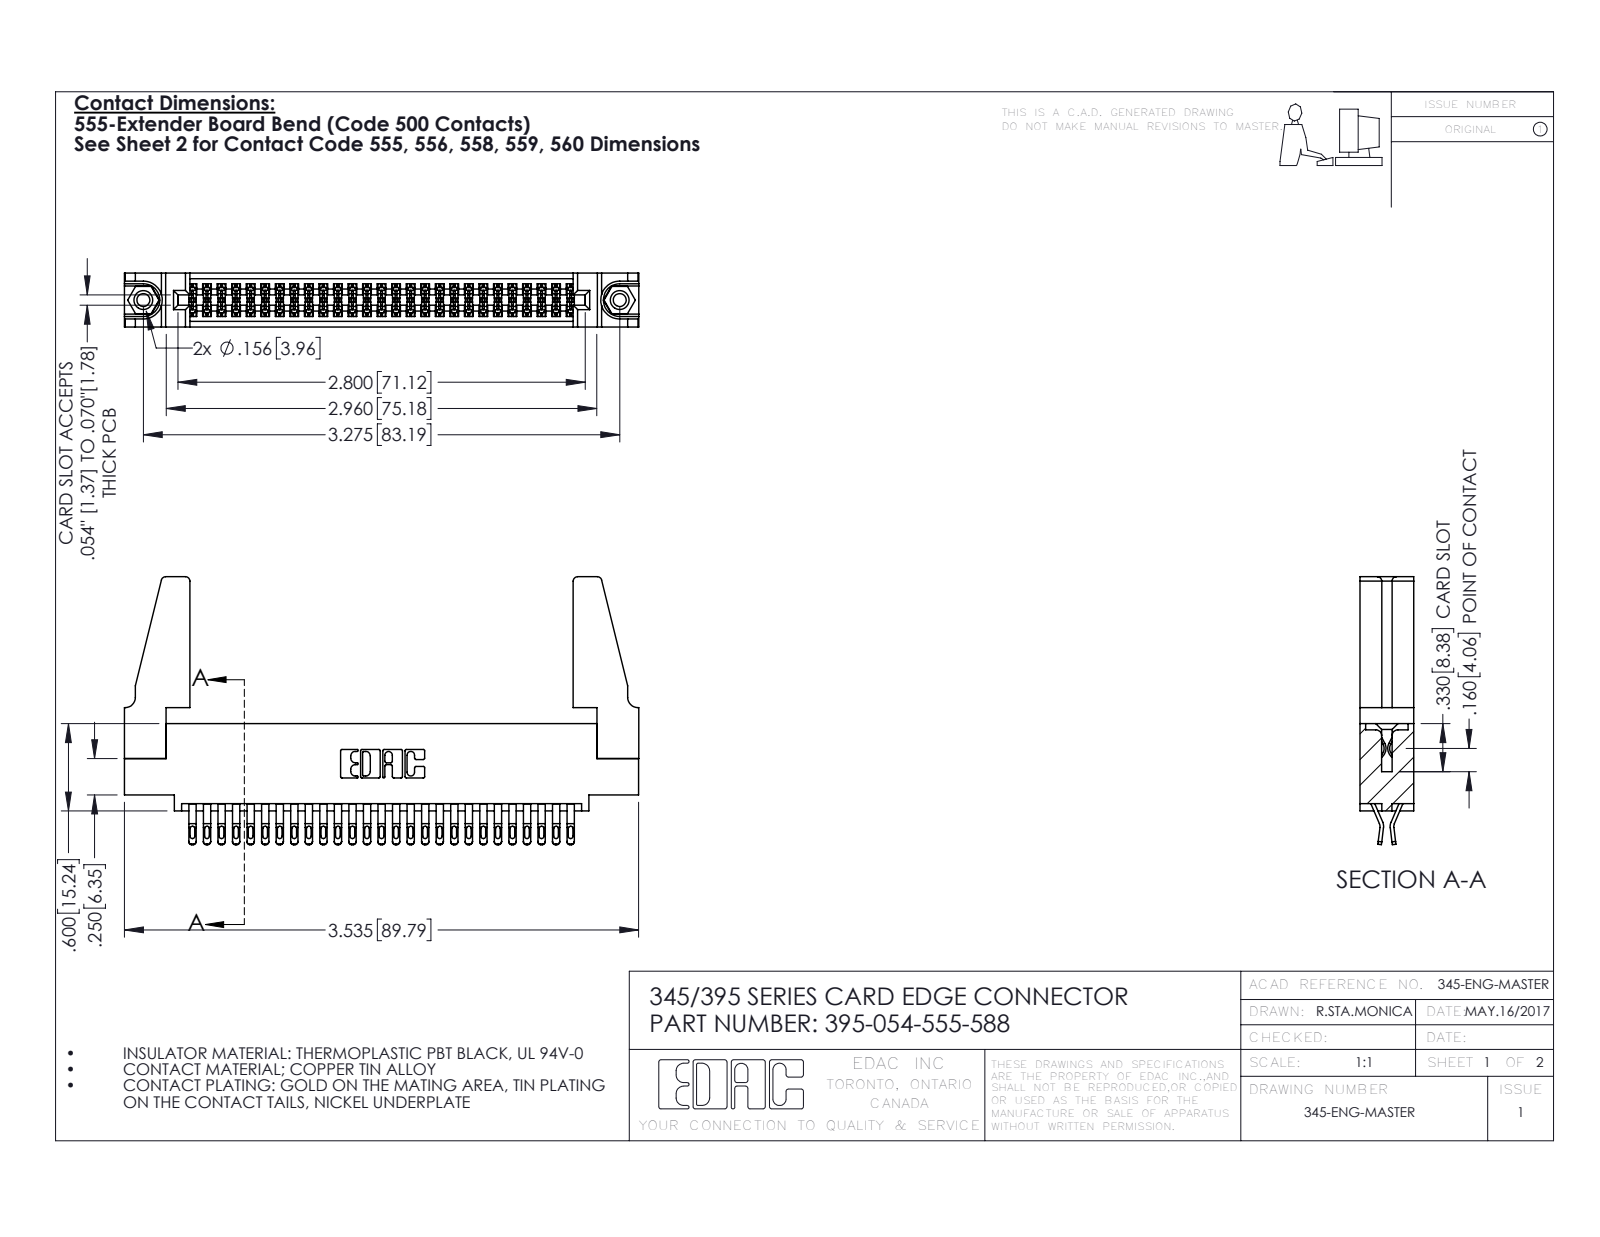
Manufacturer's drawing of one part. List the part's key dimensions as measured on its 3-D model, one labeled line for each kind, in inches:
Part name (STEP PRODUCT): 345-250-001_345-250-001-102; 345-292-001_555 Tail; 395-054-555-588; 345-220-078_345-220-088 (+1 more)
STEP written by: SolidWorks 2016 (CONFIG_CONTROL_DESIGN)
Units: inches
Bodies: 59 solids, 3278 faces (1830 planar, 1432 cylindrical, 16 other)
Overall size (bounding box): 3.536 × 1.842 × 0.37
Volume: 0.727 in³ · Surface area: 25.24 in²
Round holes (diameter × count): ⌀0.089 ×2, ⌀0.125 ×2, ⌀0.156 ×2, ⌀0.064 ×1
Round bosses / shafts (diameter × count): ⌀0.155 ×2
Partial cylindrical surfaces — rounded edges, fillets, slot ends (radius × count): R0.016 ×135, R0.02 ×108, R0.006 ×81, R0.01 ×22, R0.03 ×8, R0.007 ×6, R0.031 ×6, R0.026 ×3
Main face-to-face distances: 0.072, 0.298, 0.37, 0.025, 0.2, 0.098, 0.272, 0.225, 0.175, 0.149
Hole centre spacings: 0.27, 3.04, 3.275
